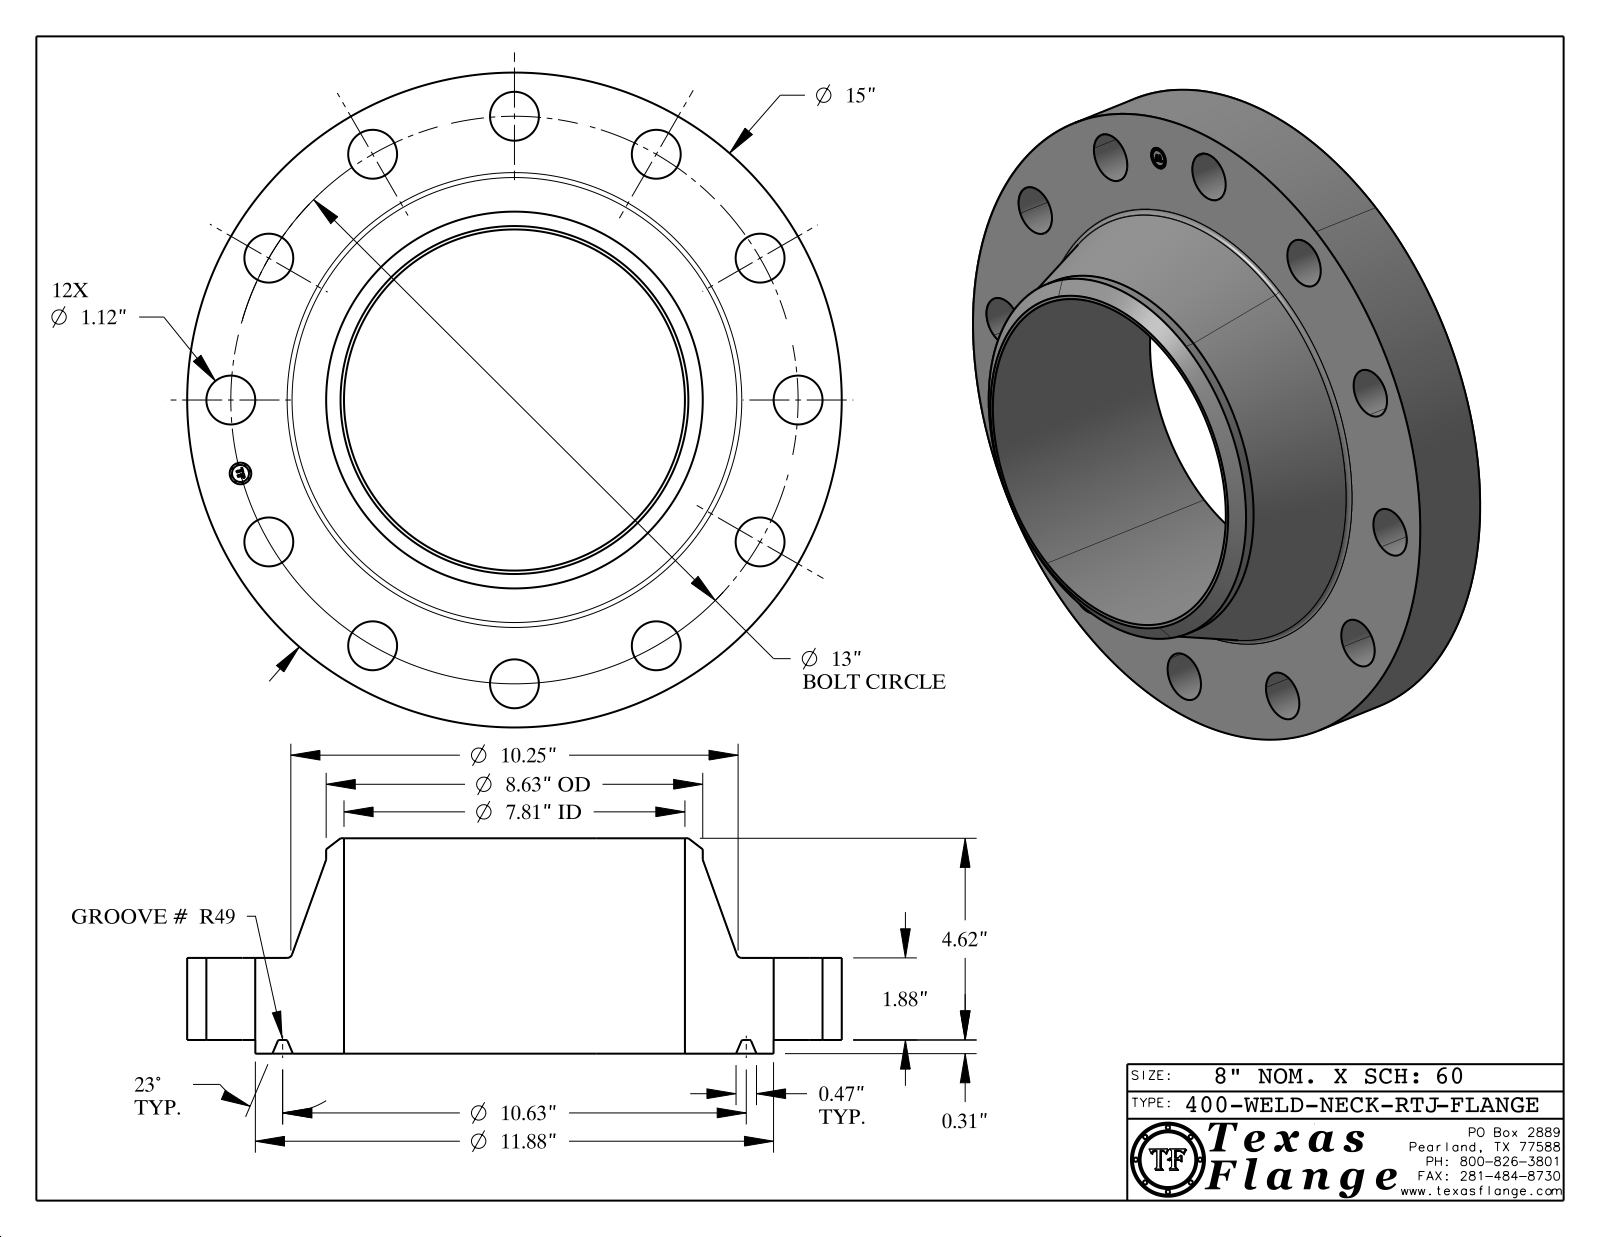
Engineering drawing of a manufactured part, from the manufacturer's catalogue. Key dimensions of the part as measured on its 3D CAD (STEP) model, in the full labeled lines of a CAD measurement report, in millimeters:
Part name (STEP PRODUCT): 400-WELD-NECK-RTJ
STEP written by: CATIA V5 STEP AP214 (AUTOMOTIVE_DESIGN)
Units: millimetres
Bodies: 1 solid, 437 faces (371 planar, 52 cylindrical, 14 other)
Overall size (bounding box): 381 × 381 × 125.3
Volume: 4 754 000 mm³ · Surface area: 389 100 mm²
Round holes (diameter × count): ⌀28.4 ×12, ⌀12.6 ×1, ⌀198.5 ×1
Round bosses / shafts (diameter × count): ⌀0.8 ×8, ⌀381 ×1, ⌀301.6 ×1, ⌀219.2 ×1, ⌀9.9 ×1
Main face-to-face distances: 47.8, 8, 55.7, 125.3, 117.3, 69.6, 55.3, 47.4, 0.4, 70
Hole centre spacings: 165.1, 85.5, 233.5, 286, 318.9, 330.2, 43.1, 126.4
